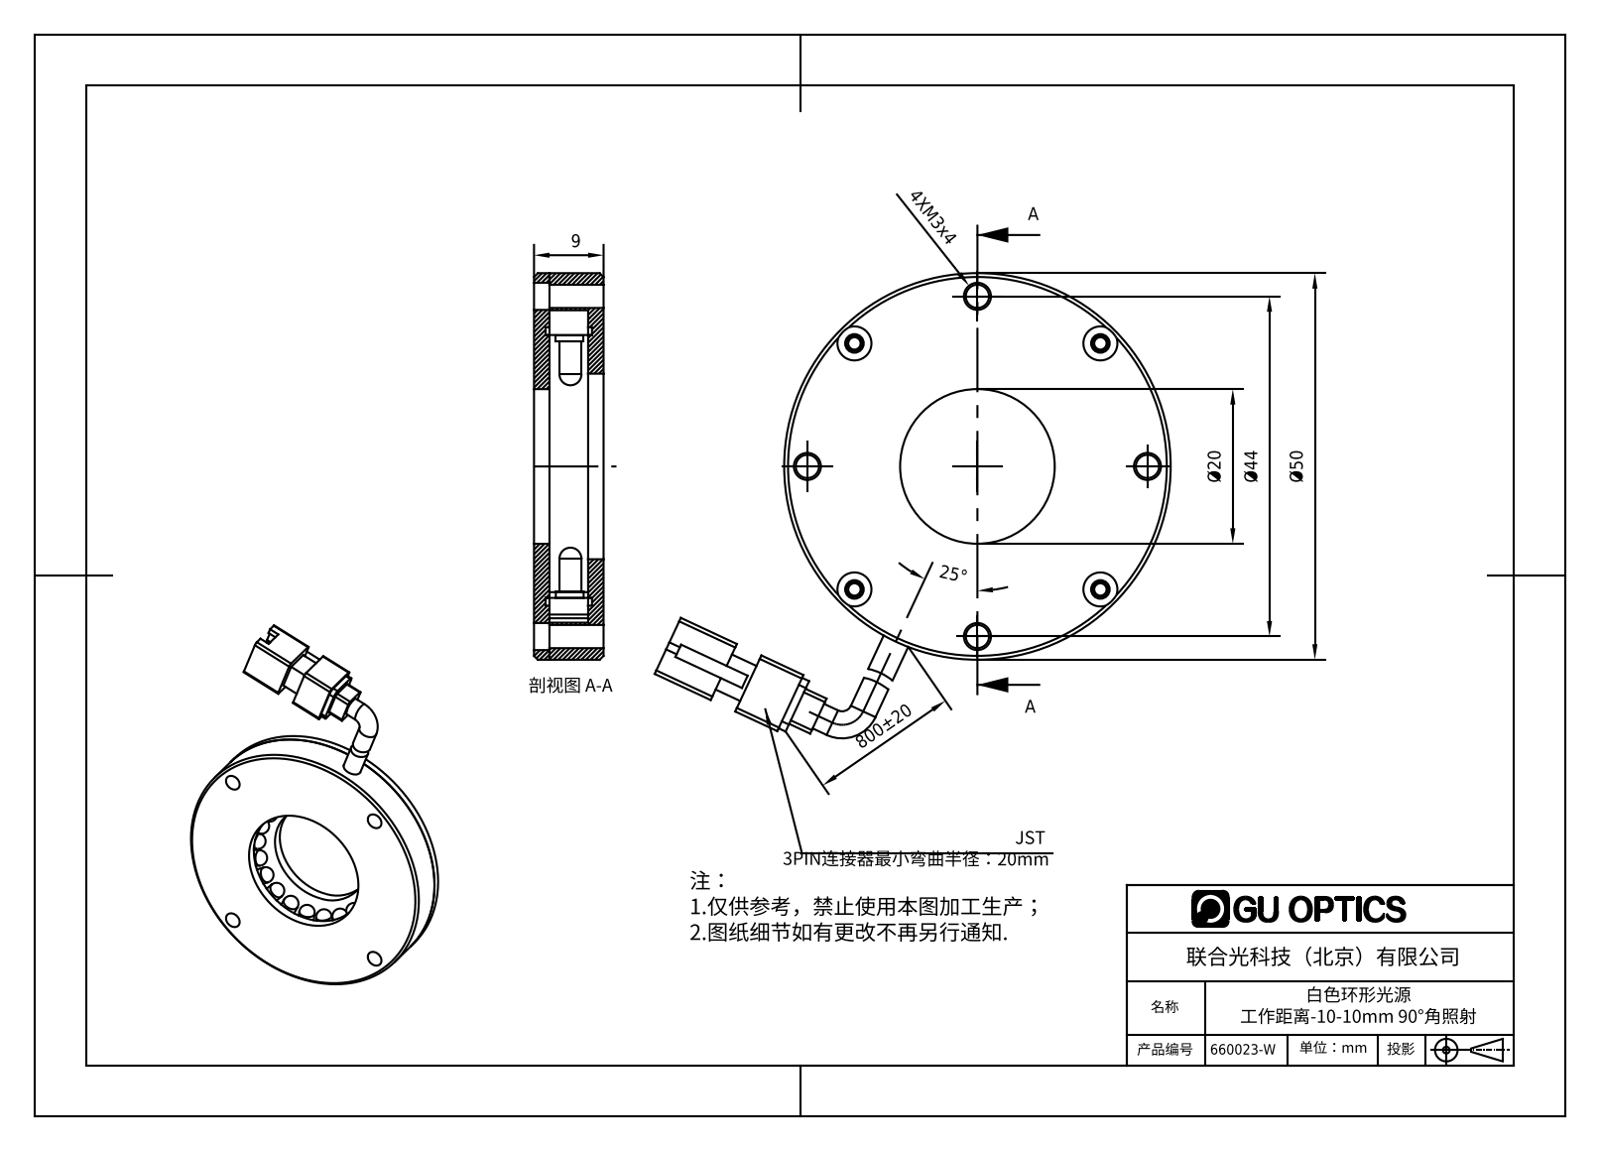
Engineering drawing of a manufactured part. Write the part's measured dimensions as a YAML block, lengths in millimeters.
part_name: "660023-W"
step_written_by: "SolidWorks 2016 (AUTOMOTIVE_DESIGN)"
units: millimeters
bodies: {solids: 26, faces: 561, planar: 329, cylindrical: 187, other: 45}
overall_size: [73.5, 50, 10]
volume: 11250
surface_area: 13403
round_holes:
  - {diameter: 3, count: 5}
  - {diameter: 3.5, count: 5}
  - {diameter: 1.6, count: 4}
  - {diameter: 2, count: 4}
  - {diameter: 2.4, count: 4}
  - {diameter: 20, count: 1}
  - {diameter: 24, count: 1}
  - {diameter: 36, count: 1}
  - {diameter: 40.4, count: 1}
round_bosses_or_shafts:
  - {diameter: 3.8, count: 21}
  - {diameter: 3, count: 21}
  - {diameter: 3.5, count: 2}
  - {diameter: 50, count: 1}
  - {diameter: 34.4, count: 1}
  - {diameter: 34, count: 1}
partial_cylinders:
  - {radius: 0.5, count: 12}
  - {radius: 1, count: 4}
face_to_face_distances: [7, 2, 9, 5, 0.5, 1, 5.5, 1.5, 6, 7.5]
hole_center_spacings: [17.04, 22.5, 31.82, 41.11, 41.12, 17.03, 22, 22.01]
